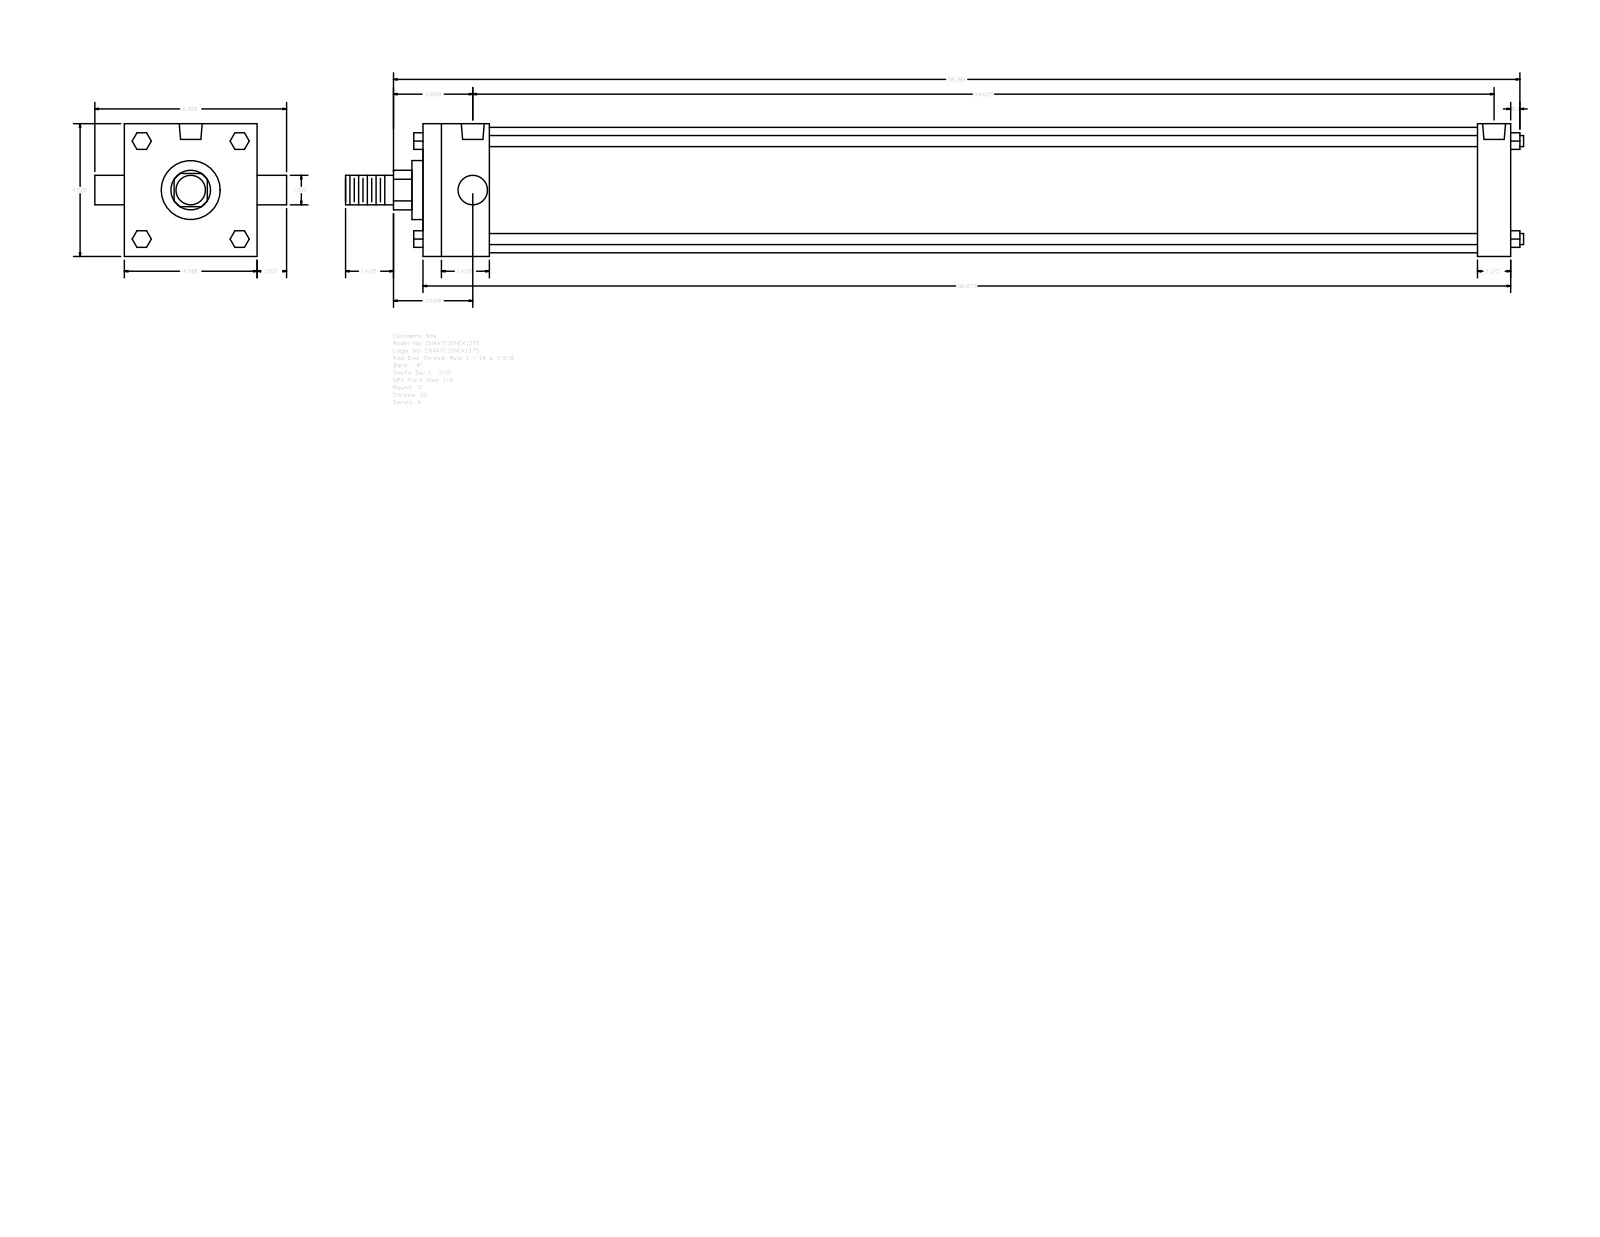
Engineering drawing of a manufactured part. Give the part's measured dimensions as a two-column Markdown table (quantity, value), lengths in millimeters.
| quantity | value |
| --- | --- |
| part name | A_TF__0400_1.375 |
| STEP written by | GSSL Pune (CONFIG_CONTROL_DESIGN) |
| units | millimeters |
| bodies | 0 solids, 120 faces (92 planar, 28 cylindrical, 0 other) |
| overall size | 1014.41 × 165.1 × 114.3 |
| round holes (diameter × count) | 8.73 × 3, 19.77 × 2 |
| round bosses / shafts (diameter × count) | 9.53 × 4, 25.4 × 2, 107.95 × 1, 50.8 × 1, 34.92 × 1 |
| partial cylindrical surfaces (radius × count) | 17.06 × 1 |
| main face-to-face distances | 114.3, 936.62, 57.15, 908.05, 28.57, 850.9, 879.47, 66.67, 14.29, 25.4 |
| hole center spacings | 3.18, 876.3, 873.12, 879.48 |
